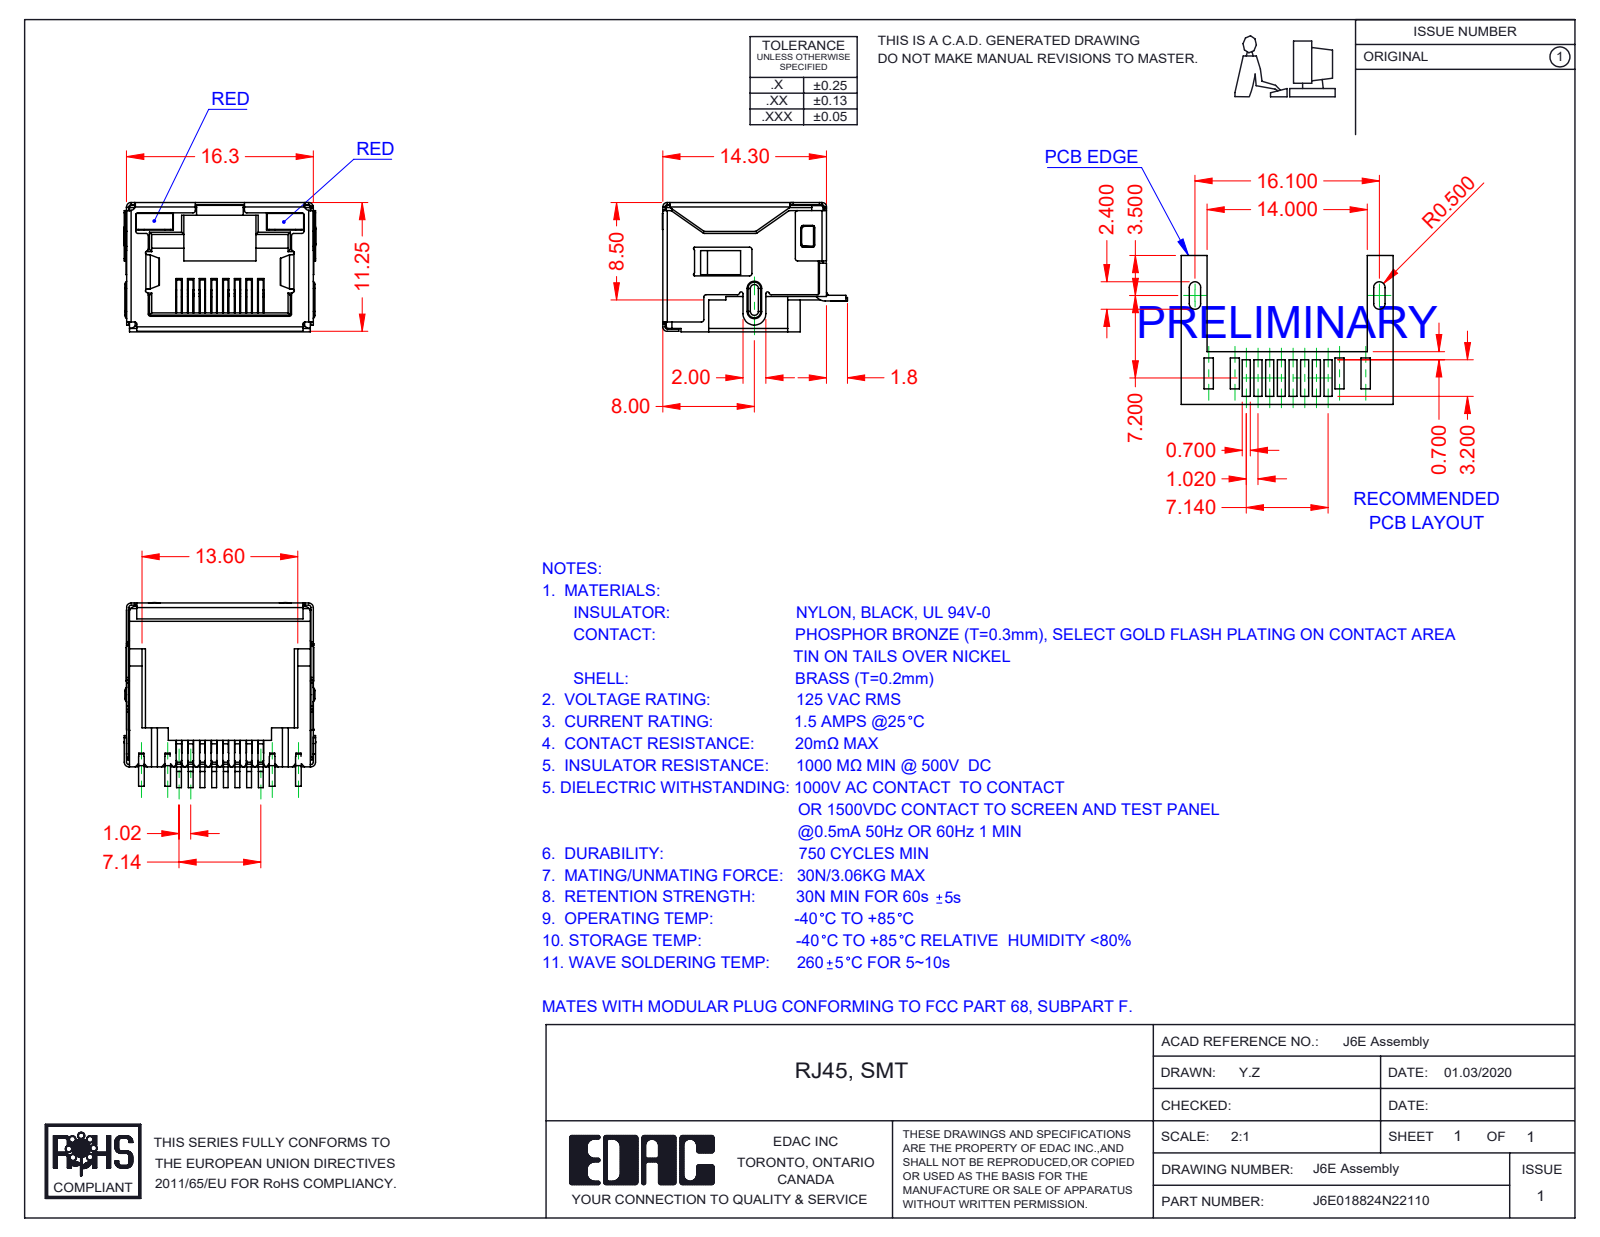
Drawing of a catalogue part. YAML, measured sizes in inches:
part_name: "6E Shield_LED; 6E Contacts; 6E LED RH_2-Red; 6E LED LH_2-Red (+2 more)"
step_written_by: "SolidWorks 2016 (CONFIG_CONTROL_DESIGN)"
units: inches
bodies: {solids: 12, faces: 1496, planar: 1099, cylindrical: 347, other: 50}
overall_size: [0.659, 0.636, 0.445]
volume: 0.068
surface_area: 6.27
partial_cylinders:
  - {radius: 0.008, count: 82}
  - {radius: 0.01, count: 17}
  - {radius: 0.016, count: 13}
  - {radius: 0.02, count: 13}
  - {radius: 0.004, count: 10}
  - {radius: 0.006, count: 7}
  - {radius: 0.012, count: 4}
  - {radius: 0.039, count: 3}
face_to_face_distances: [0.435, 0.632, 0.634, 0.624, 0.437, 0.445, 0.094, 0.028, 0.388, 0.019]
